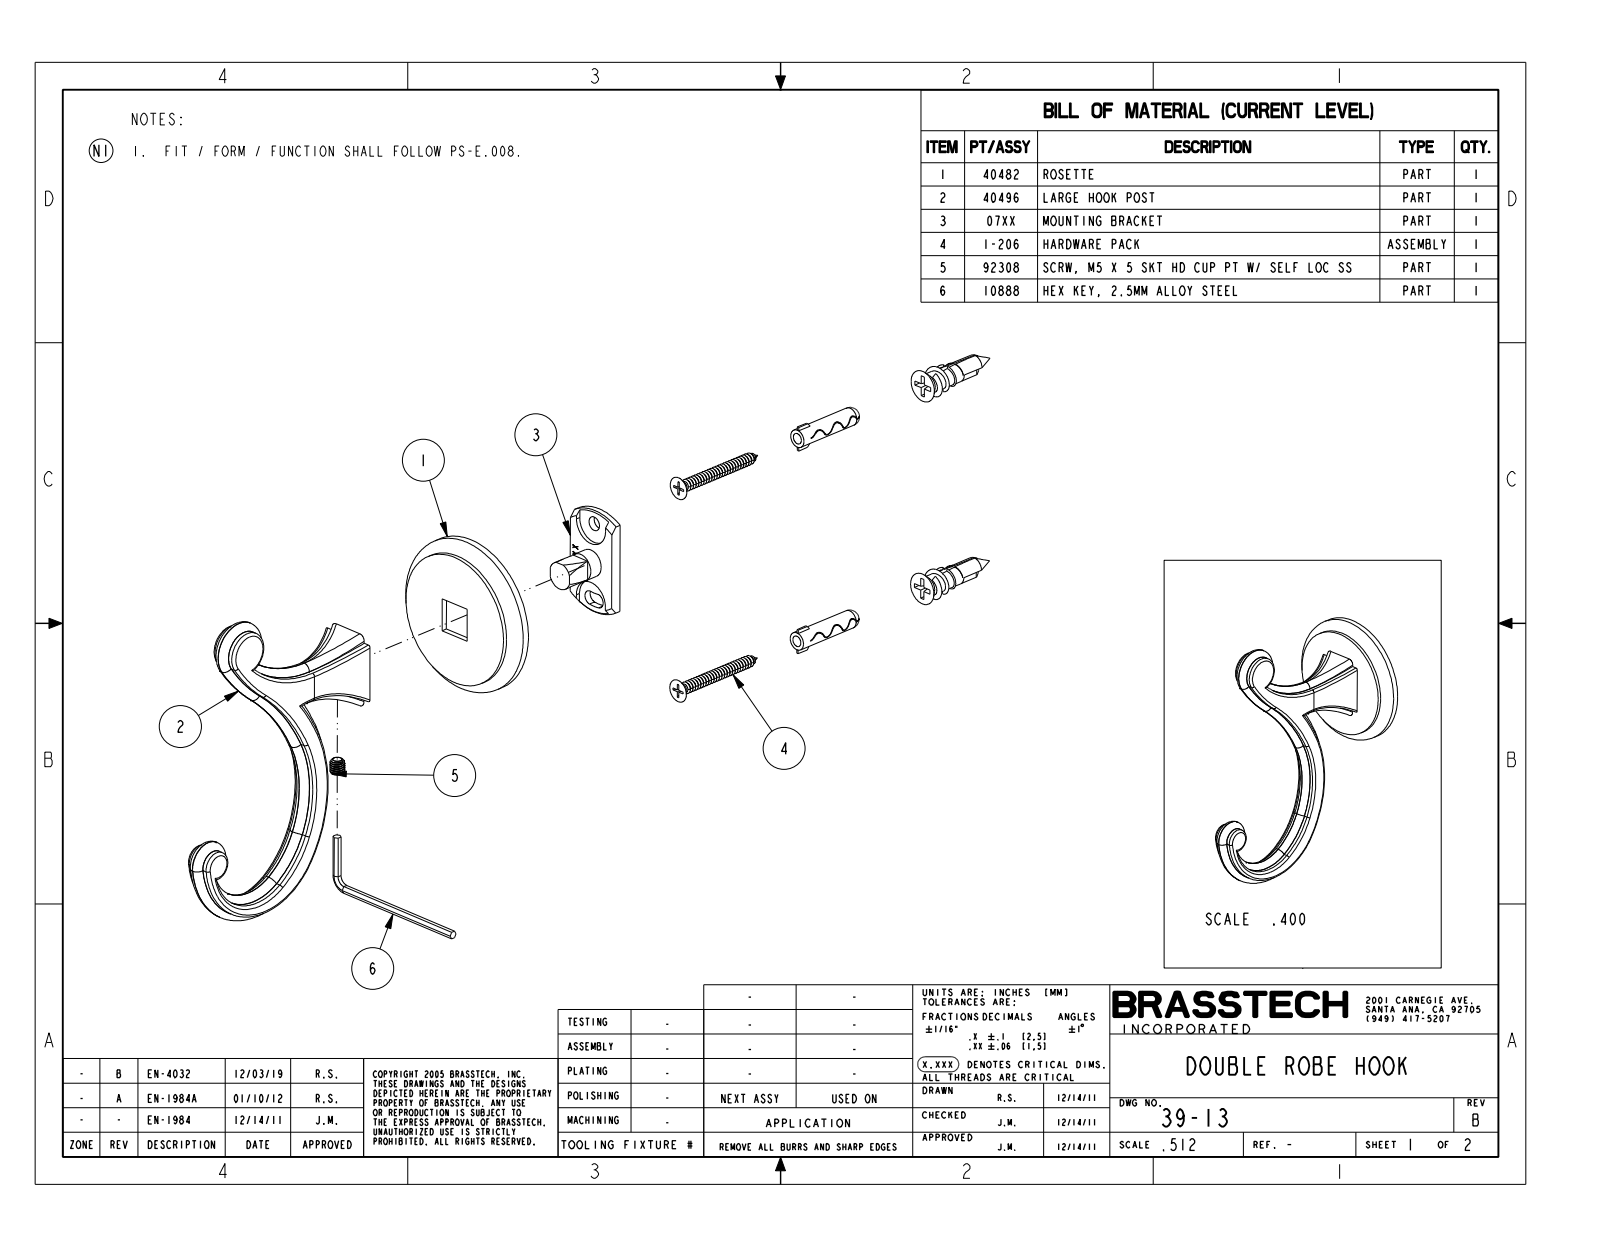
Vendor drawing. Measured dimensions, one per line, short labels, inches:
name: 39-13_WEB
written by: PRO/ENGINEER BY PARAMETRIC TECHNOLOGY CORPORATION, 2009300 (CONFIG_CONTROL_DESIGN)
unit: in
bodies: 0 solids, 110 faces (6 planar, 46 cylindrical, 58 other)
size: 4.436 × 3.251 × 2.165
bosses: 1× ⌀2.165, 1× ⌀1.85
rounds: 4× R1.673, 2× R1.181, 2× R1.575, 2× R1.772, 1× R0.197, 1× R0.295, 1× R0.296, 1× R0.394
face distances: 0.315, 0.395, 0.099, 0.296, 0.197
